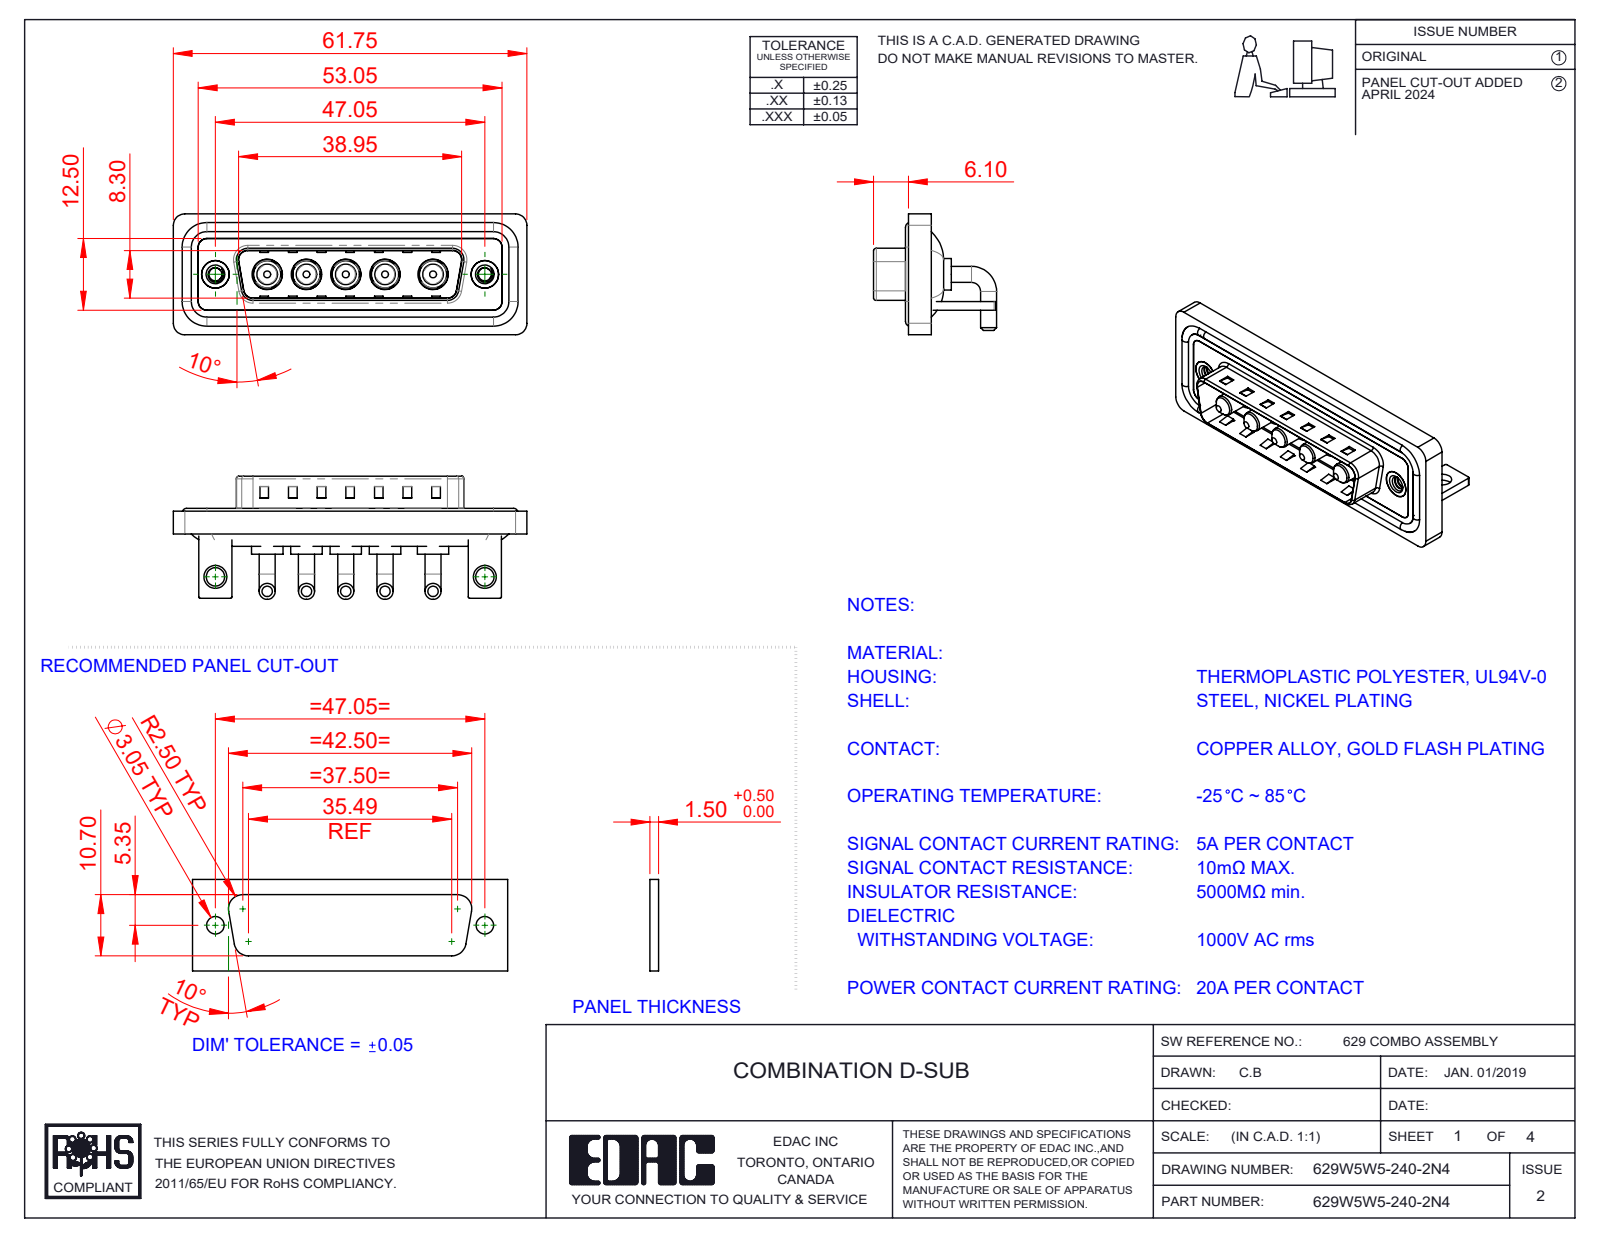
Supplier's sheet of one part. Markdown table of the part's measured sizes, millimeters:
| quantity | value |
| --- | --- |
| part name | 629W5W5-240-2N4; 629Combo Housing_5W5; 629Combo Shell Rear_25 Contacts; 629Combo Waterproof Housing_25 Contacts (+4 more) |
| STEP written by | SolidWorks 2023 (CONFIG_CONTROL_DESIGN) |
| units | millimeters |
| bodies | 19 solids, 738 faces (279 planar, 311 cylindrical, 148 other) |
| overall size | 61.75 × 21.5 × 21.1 |
| volume | 8 079 mm³ |
| surface area | 12 858 mm² |
| round holes (diameter × count) | 4.85 × 5, 5.3 × 5, 2.26 × 2, 3.2 × 2, 4 × 2, 4.8 × 2, 5 × 2 |
| round bosses / shafts (diameter × count) | 2.8 × 10, 5.5 × 5, 5.2 × 5, 4.75 × 5, 3.75 × 5, 3.6 × 5, 1.6 × 4, 4.9 × 2 |
| partial cylindrical surfaces (radius × count) | 2 × 19, 1.5 × 18, 0.25 × 16, 0.5 × 9, 1.6 × 8, 2.1 × 5, 0.6 × 4, 0.65 × 4 |
| main face-to-face distances | 0.4, 1.5, 2.9, 0.8, 2.1, 1.1, 3.7, 4.5, 4.1, 1.2 |
| hole center spacings | 6.86, 13.73, 47.05, 6.85, 6.87, 8.37, 8.38, 9.04 |
